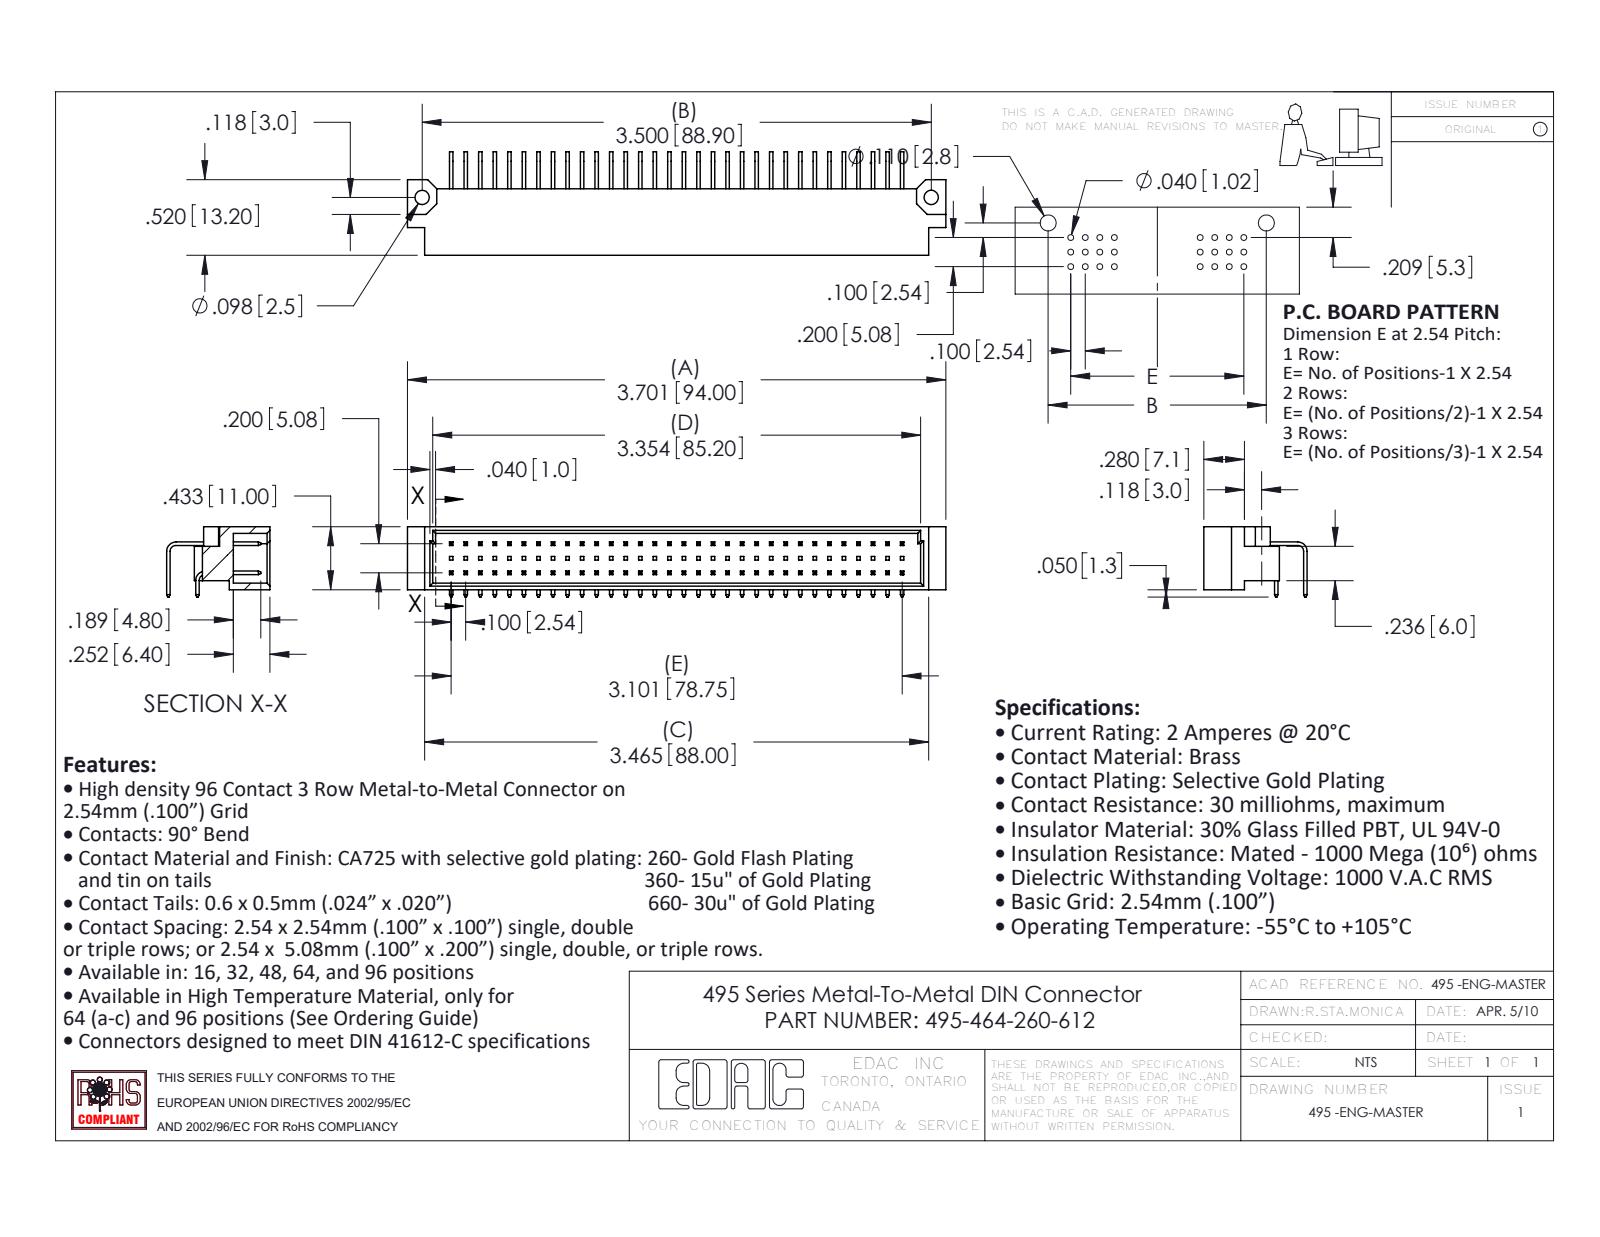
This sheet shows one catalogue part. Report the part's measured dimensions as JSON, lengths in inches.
{"part_name": "495-464-260-612; 495-290-1; 495-290-3; 495 Part_96", "step_written_by": "SolidWorks 2020 (AUTOMOTIVE_DESIGN)", "units": "inches", "bodies": {"solids": 65, "faces": 1585, "planar": 1453, "cylindrical": 132, "other": 0}, "overall_size": [3.701, 0.711, 0.483], "volume_in3": 0.39, "surface_area_in2": 15.36, "round_holes": [[0.098, 2]], "partial_cylinders_radius": [[0.04, 2], [0.065, 2]], "face_to_face_distances": [0.045, 0.388, 0.024, 0.2, 0.205, 0.433, 0.1, 0.343, 0.063, 0.37], "hole_center_spacings": [3.5]}
